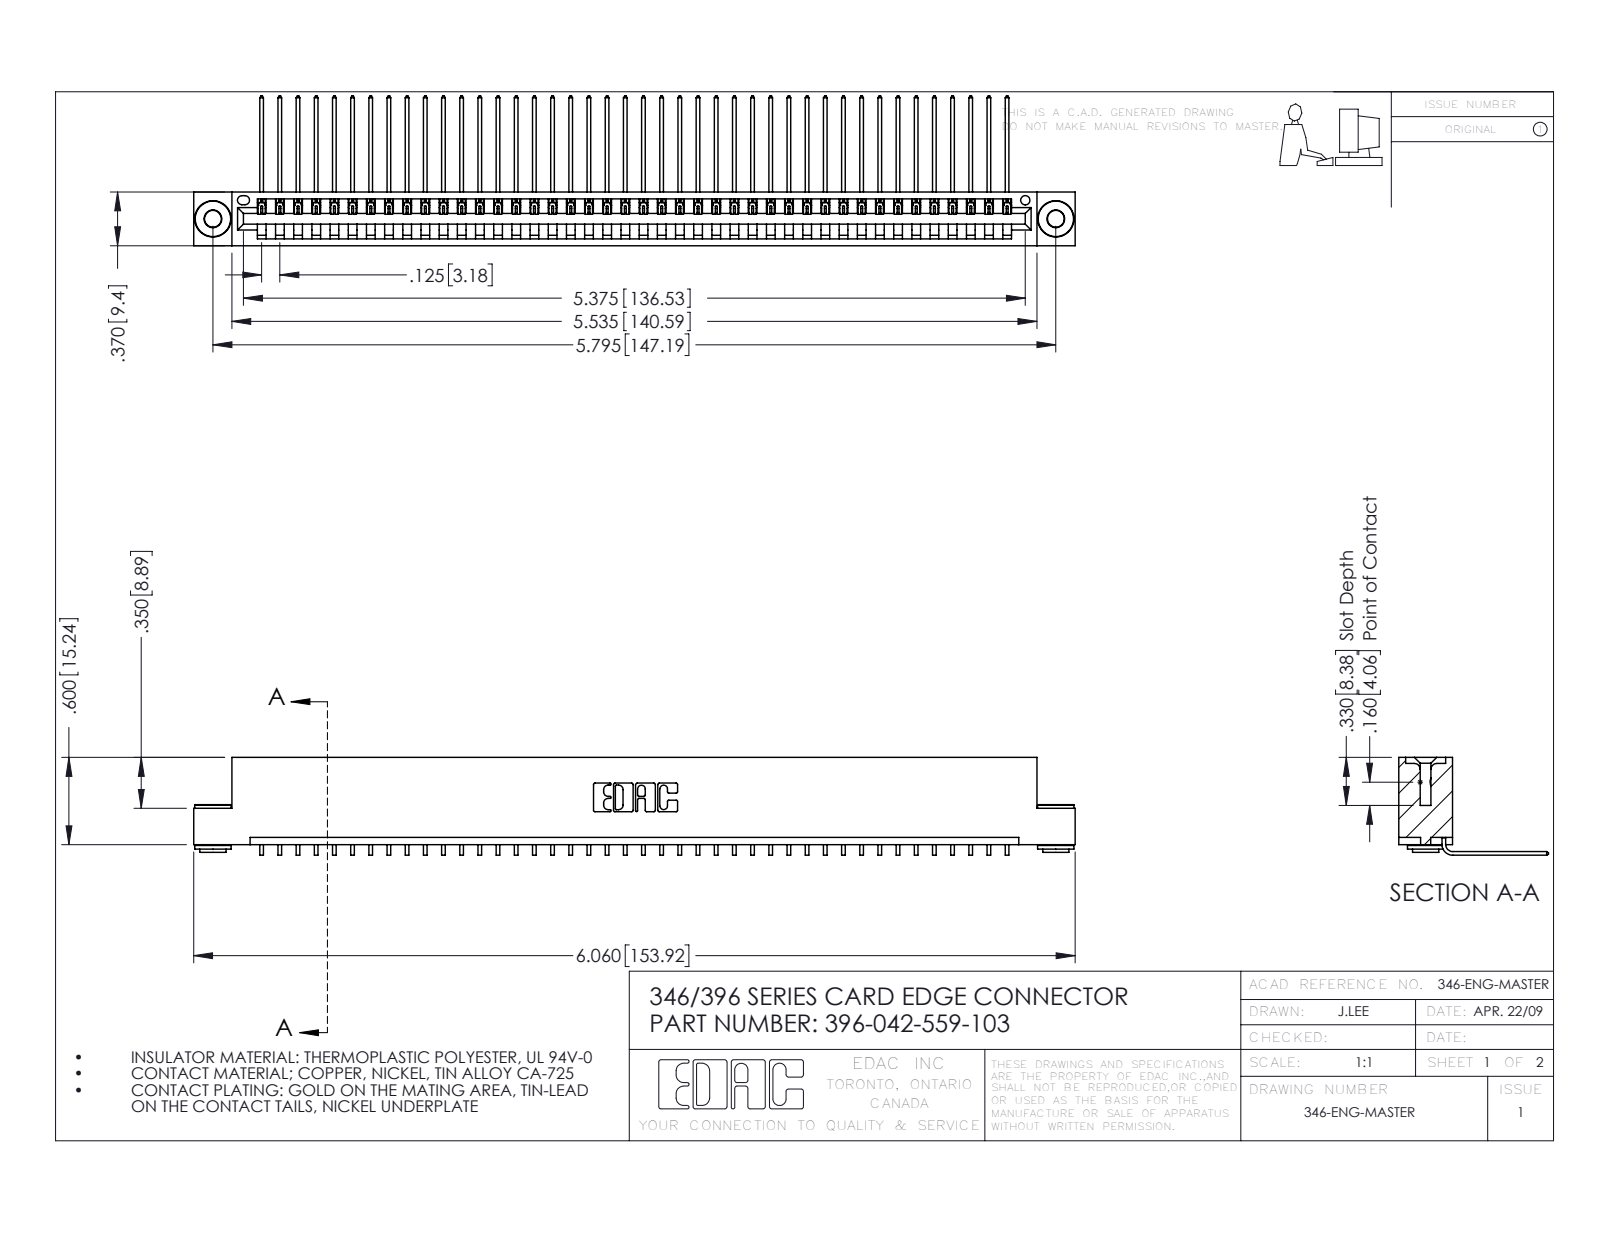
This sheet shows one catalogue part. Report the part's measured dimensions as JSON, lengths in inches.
{"part_name": "345-292-001_558 559 Tail - 1; 396-042-559-103; 345-250-002_345-250-002-102; 346 Part_Flush Mounting Lugs - 0.156 Dia-TH", "step_written_by": "SolidWorks 2016 (CONFIG_CONTROL_DESIGN)", "units": "inches", "bodies": {"solids": 45, "faces": 2680, "planar": 1850, "cylindrical": 822, "other": 8}, "overall_size": [6.06, 1.03, 0.673], "volume_in3": 0.909, "surface_area_in2": 30.49, "round_holes": [[0.116, 2], [0.156, 2], [0.064, 1]], "round_bosses_or_shafts": [[0.25, 2], [0.18, 2], [0.136, 2]], "partial_cylinders_radius": [[0.006, 84], [0.01, 22], [0.007, 6], [0.031, 6], [0.026, 3], [0.031, 2], [0.04, 2], [0.014, 1]], "face_to_face_distances": [0.048, 0.322, 0.37, 0.25, 0.025, 0.072, 0.298, 0.148, 0.222, 0.1], "hole_center_spacings": [0.246, 5.586, 5.795]}
